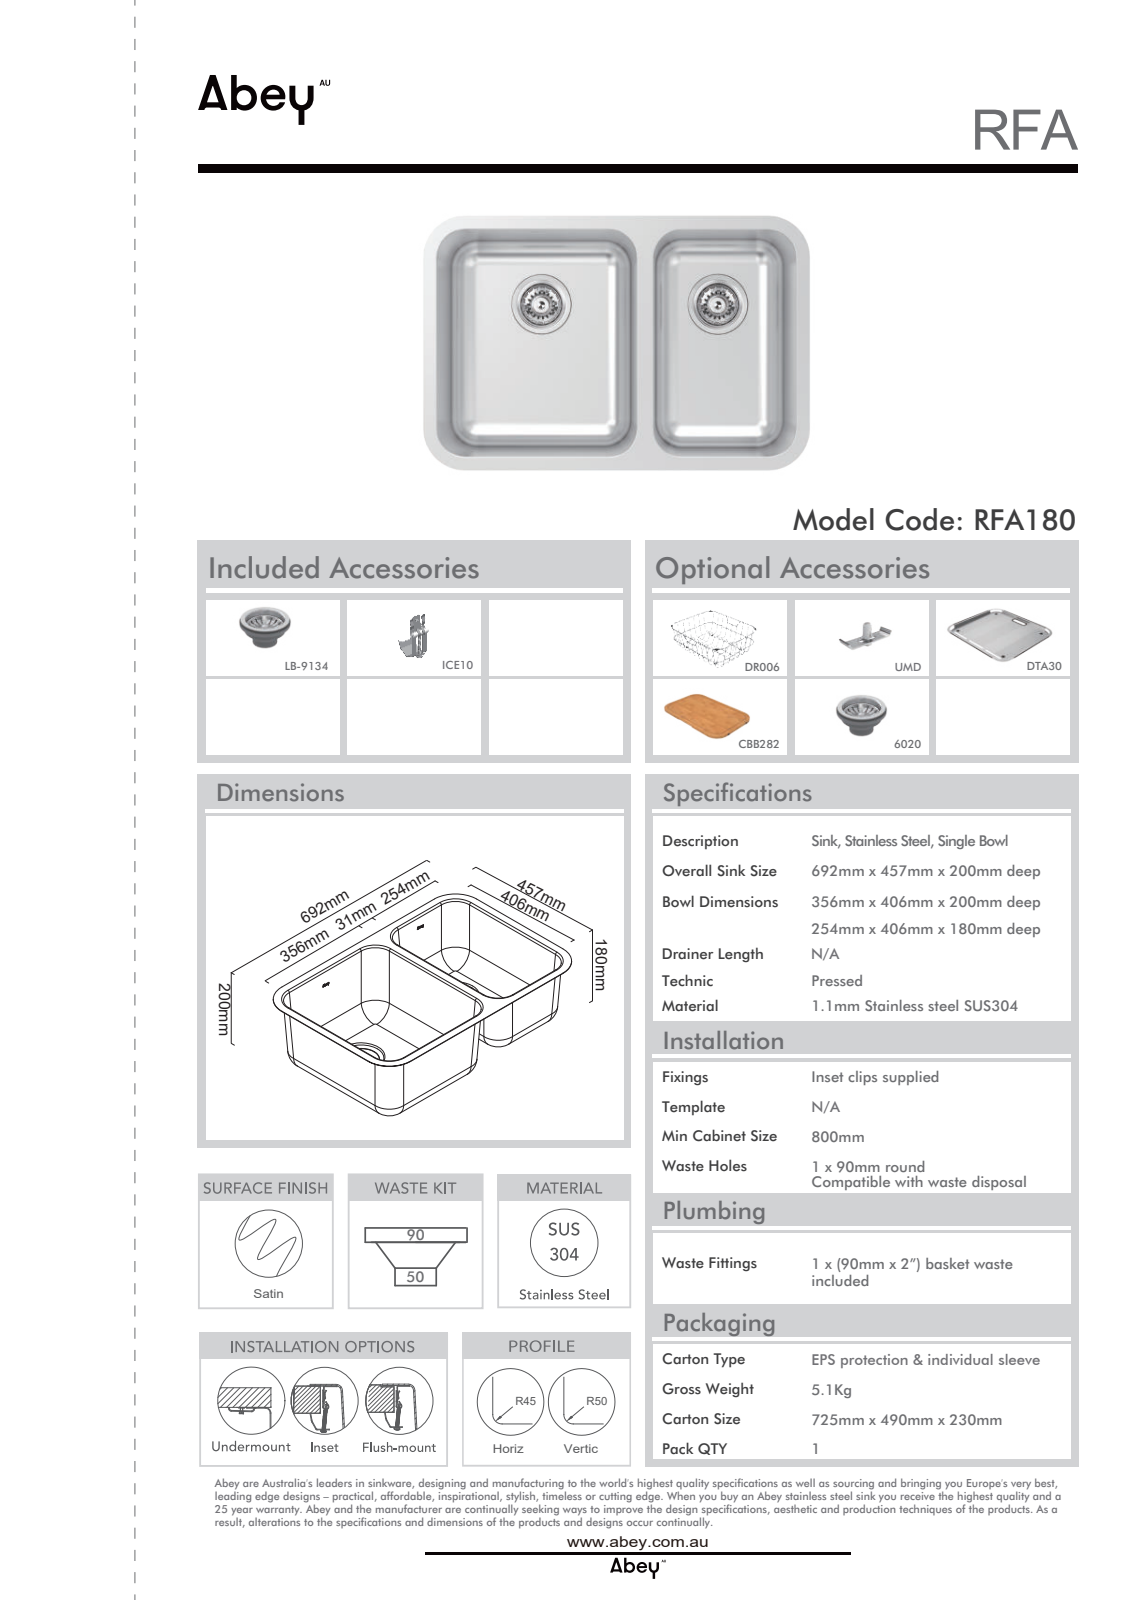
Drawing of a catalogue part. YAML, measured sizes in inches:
part_name: "RFA180"
step_written_by: "SolidWorks 2022 (CONFIG_CONTROL_DESIGN)"
units: inches
bodies: {solids: 1, faces: 136, planar: 24, cylindrical: 56, other: 56}
overall_size: [27.244, 17.992, 8.268]
volume: 44.53
surface_area: 2238
round_holes:
  - {diameter: 3.587, count: 2}
partial_cylinders:
  - {radius: 1.772, count: 8}
  - {radius: 1.811, count: 8}
  - {radius: 1.969, count: 8}
  - {radius: 2.008, count: 8}
  - {radius: 0.157, count: 6}
  - {radius: 0.197, count: 6}
  - {radius: 2.953, count: 4}
face_to_face_distances: [0.039, 11.209, 15.221, 11.249, 11.17, 15.26, 15.181, 17.992, 27.244, 7.441]
hole_center_spacings: [13.228]
